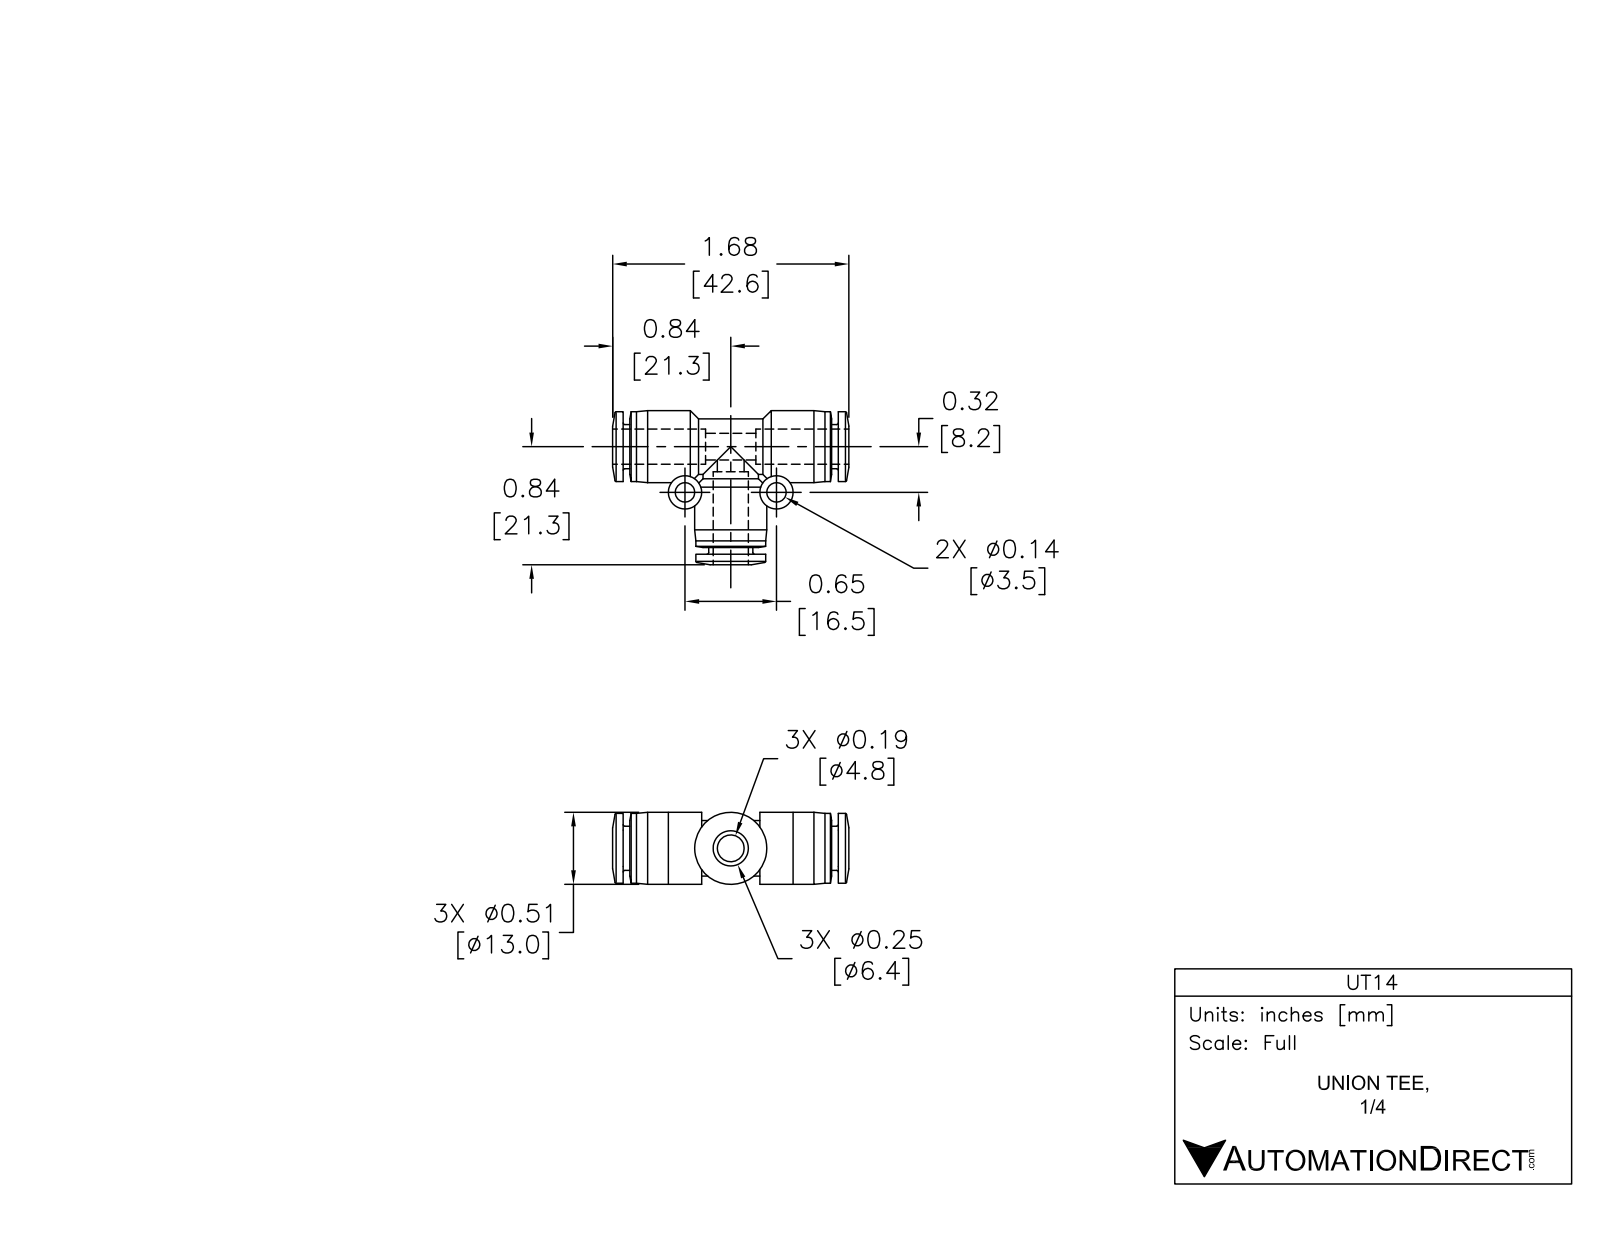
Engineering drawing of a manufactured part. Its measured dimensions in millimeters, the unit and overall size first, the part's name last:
Units: millimetres
Overall size (bounding box): 42.6 × 27.8 × 13
Round holes (diameter × count): ⌀3.5 ×2, ⌀4.8 ×2, ⌀6.6 ×2
Round bosses / shafts (diameter × count): ⌀13 ×2, ⌀12.6 ×2, ⌀10 ×2, ⌀8 ×2, ⌀6 ×2
Main face-to-face distances: 1.2, 38.8, 37.6, 14.9, 13.7, 13, 23.9, 22.7, 36.4, 9
Hole centre spacings: 16.5
Volume: 5 110 mm³ · Surface area: 4 701 mm²
Bodies: 1 solid, 109 faces (13 planar, 48 cylindrical, 48 other)
Part name (STEP PRODUCT): UT14
STEP written by: SolidWorks 2015 (AUTOMOTIVE_DESIGN)
